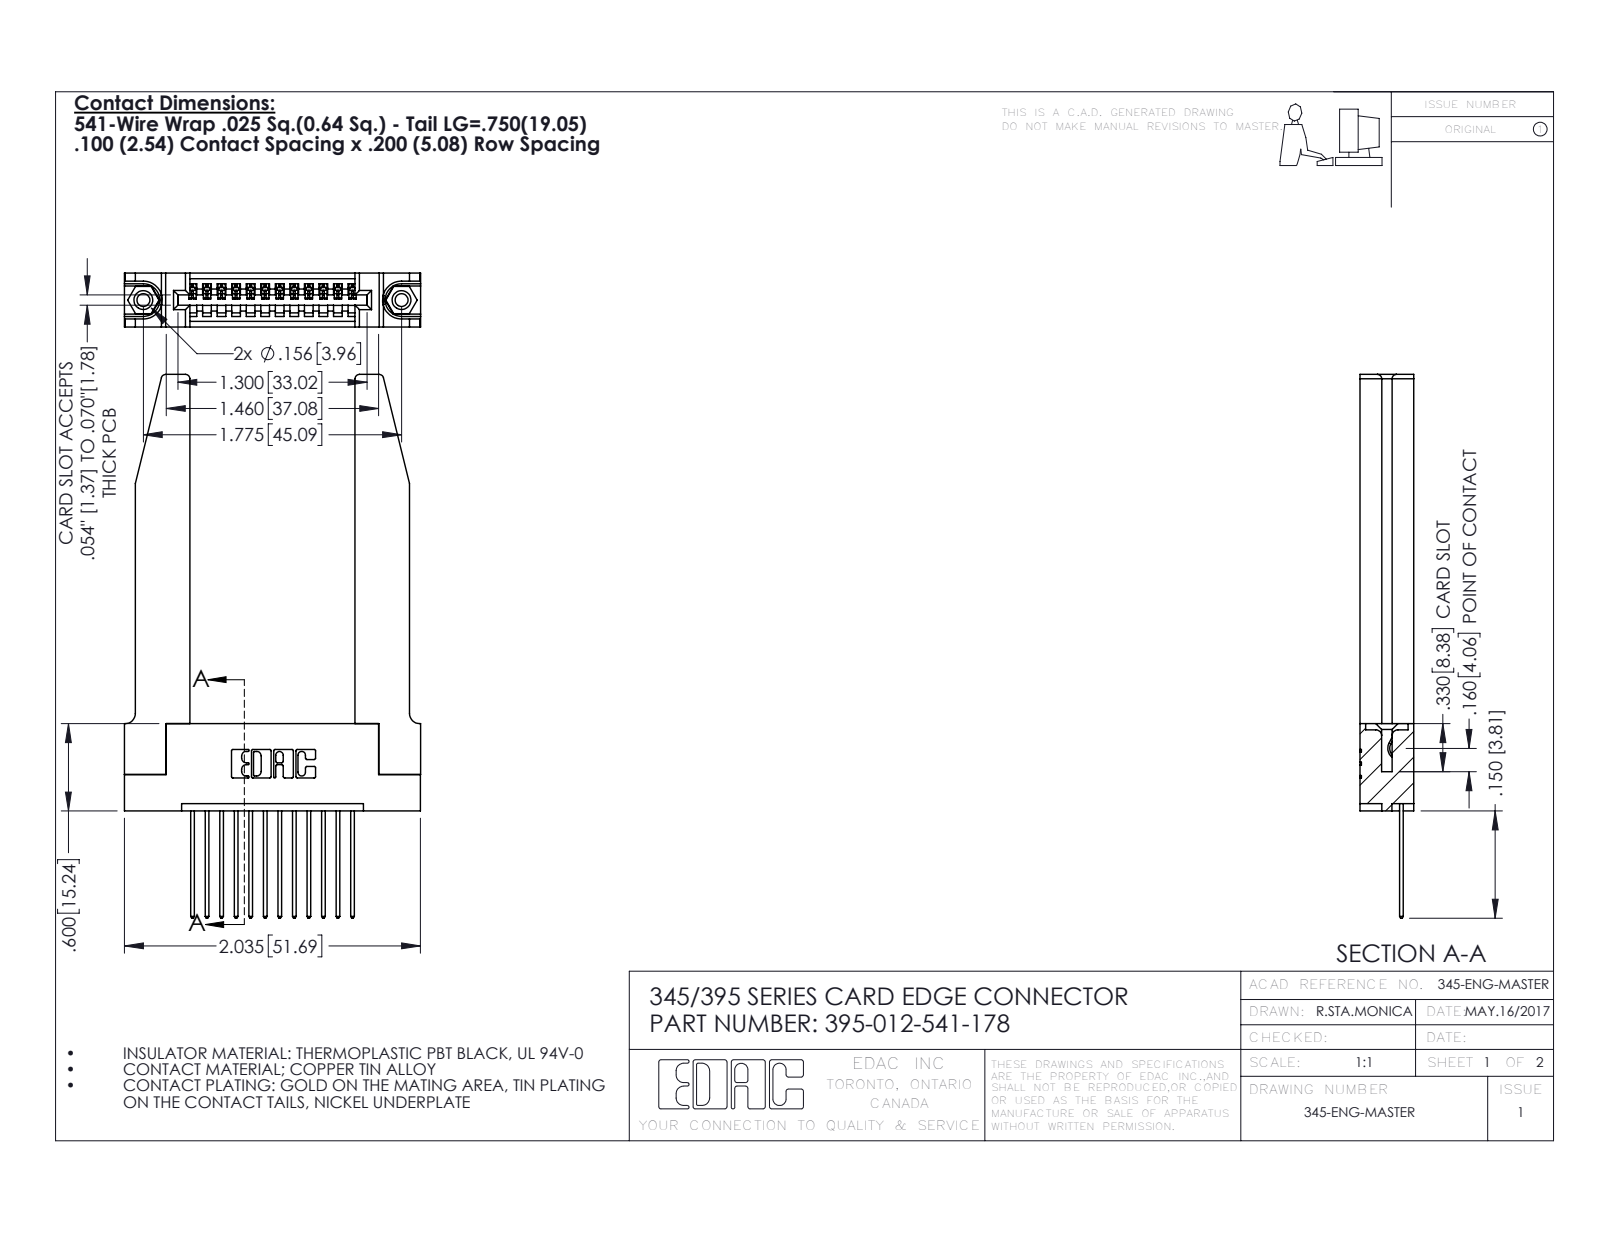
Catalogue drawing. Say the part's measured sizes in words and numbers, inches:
The part is named "345 Part_Flush Mounting Lugs - 0.156 Dia-TH; 345-250-001_345-250-001-102; 395-012-541-178; 345-220-078_345-220-078 (+1 more)". Its 3-D file was written by "SolidWorks 2016 (CONFIG_CONTROL_DESIGN)". It is 17 solids with 1056 faces: 702 planar, 302 cylindrical and 52 other. Overall it measures 3.737 by 2.036 by 0.37 inches. Its volume is 0.761 cubic inches and its surface area 20.03 square inches. Round holes: 2 of diameter 0.089, 2 of diameter 0.125, 2 of diameter 0.156, 1 of diameter 0.064. Round bosses or shafts: 2 of diameter 0.155. Partial cylindrical surfaces (rounded edges, fillets, slot ends): 24 of radius 0.006, 24 of radius 0.01, 22 of radius 0.01, 8 of radius 0.03, 6 of radius 0.007, 6 of radius 0.031, 3 of radius 0.026, 2 of radius 0.031. The main face-to-face distances are 0.37, 0.072, 0.298, 0.2, 0.15, 0.148, 0.077, 0.22, 0.098, 0.272. The hole center spacings are 0.27, 1.543, 1.775.
